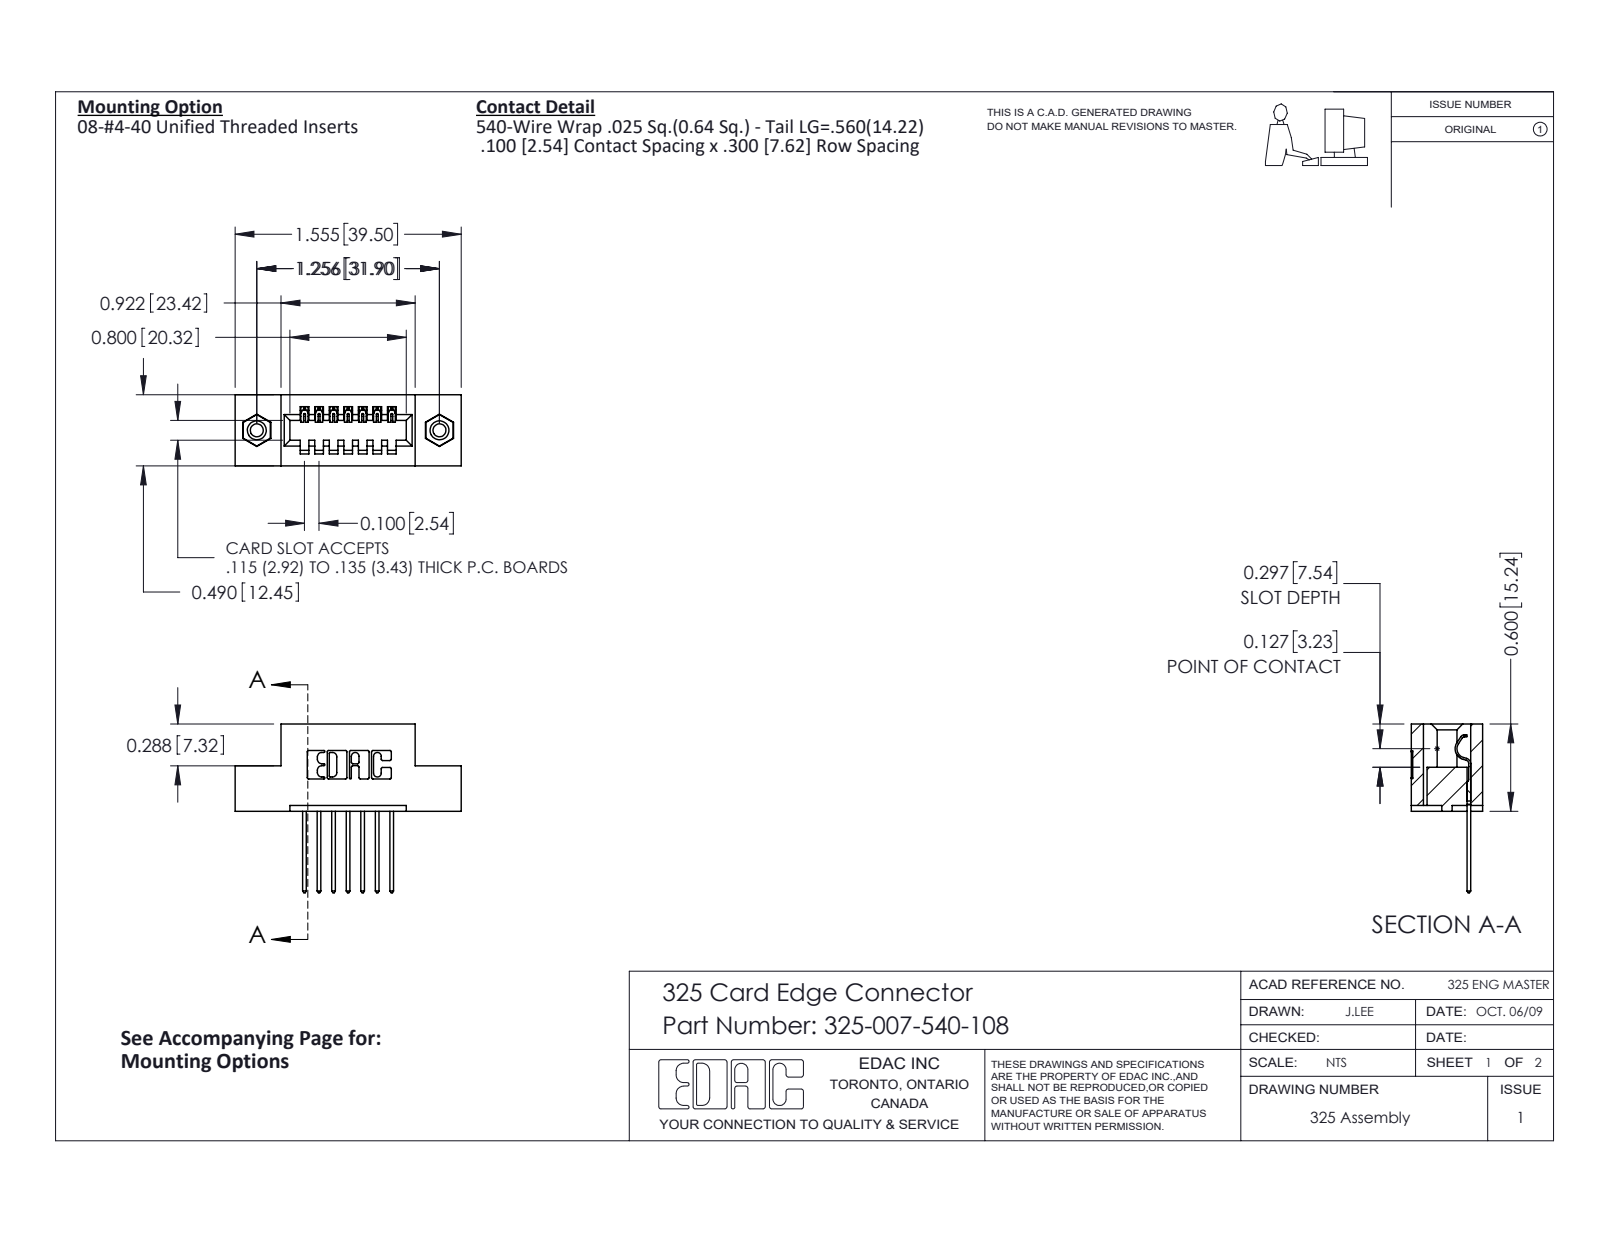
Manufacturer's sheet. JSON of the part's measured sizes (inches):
{"part_name": "325 Part_TI; 325-007-540-108; 345-250-001_345-250-003-102; 325-292-001_325-293-140", "step_written_by": "SolidWorks 2016 (CONFIG_CONTROL_DESIGN)", "units": "inches", "bodies": {"solids": 10, "faces": 580, "planar": 396, "cylindrical": 168, "other": 16}, "overall_size": [1.555, 1.16, 0.49], "volume_in3": 0.289, "surface_area_in2": 7.242, "round_holes": [[0.089, 2], [0.125, 2], [0.16, 2]], "round_bosses_or_shafts": [[0.155, 2]], "partial_cylinders_radius": [[0.01, 22], [0.006, 14], [0.01, 14], [0.007, 6], [0.031, 6], [0.026, 3], [0.014, 1], [0.022, 1]], "face_to_face_distances": [0.3, 0.1, 0.2, 0.04, 0.083, 0.407, 0.49, 0.06, 0.16, 0.4], "hole_center_spacings": [1.256]}
